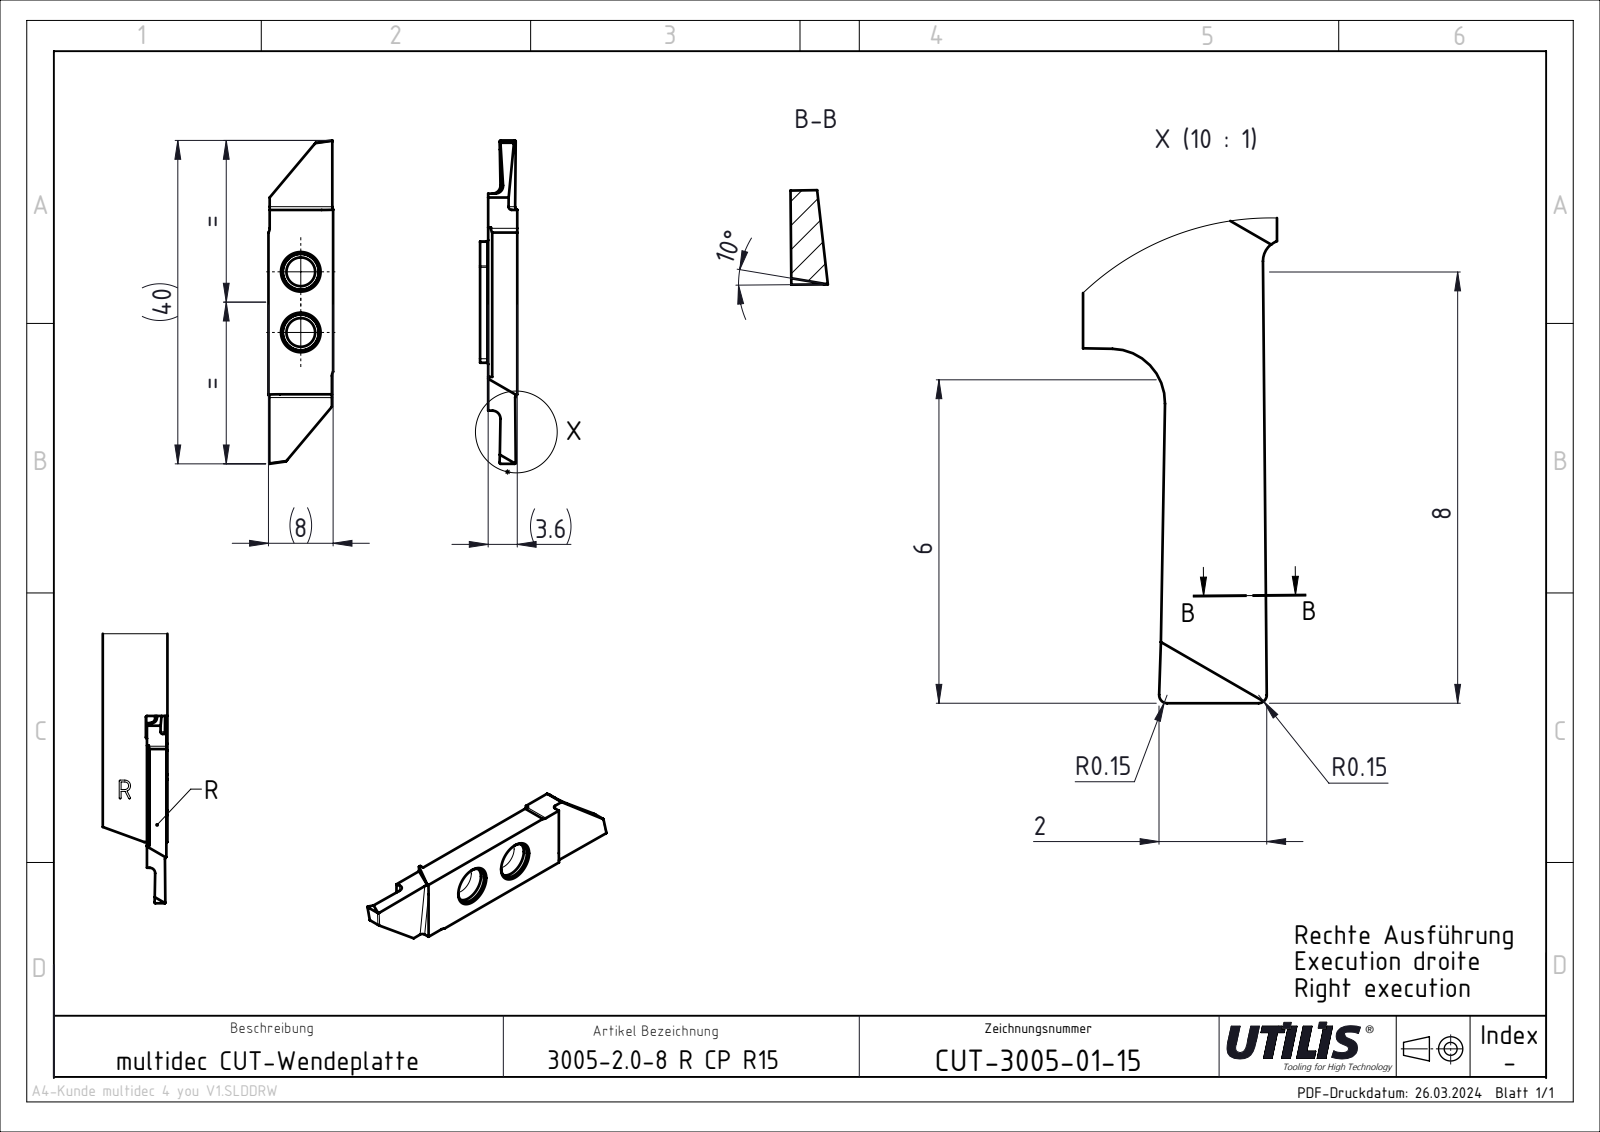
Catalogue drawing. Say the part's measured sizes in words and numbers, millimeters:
The part is named "CUT-3005 CP; ASME Y14.5". Its 3-D file was written by "SolidWorks 2023 SP4 || FormatWorks Professional (AP242_MANAGED_MODEL_BASED_3D_ENGINEERING_MIM_LF)". It is 1 solid with 36 faces: 22 planar, 14 cylindrical and 0 other. Overall it measures 40 by 8 by 3.6 millimeters. Its volume is 804 cubic millimeters and its surface area 856 square millimeters. Round holes: 2 of diameter 3.55. Partial cylindrical surfaces (rounded edges, fillets, slot ends): 4 of radius 0.15, 4 of radius 1, 2 of radius 0.4. The main face-to-face distances are 3.6, 8, 7.85, 22.54, 7.7, 40, 10.75, 29.25, 18.5. The hole center spacings are 7.49.
